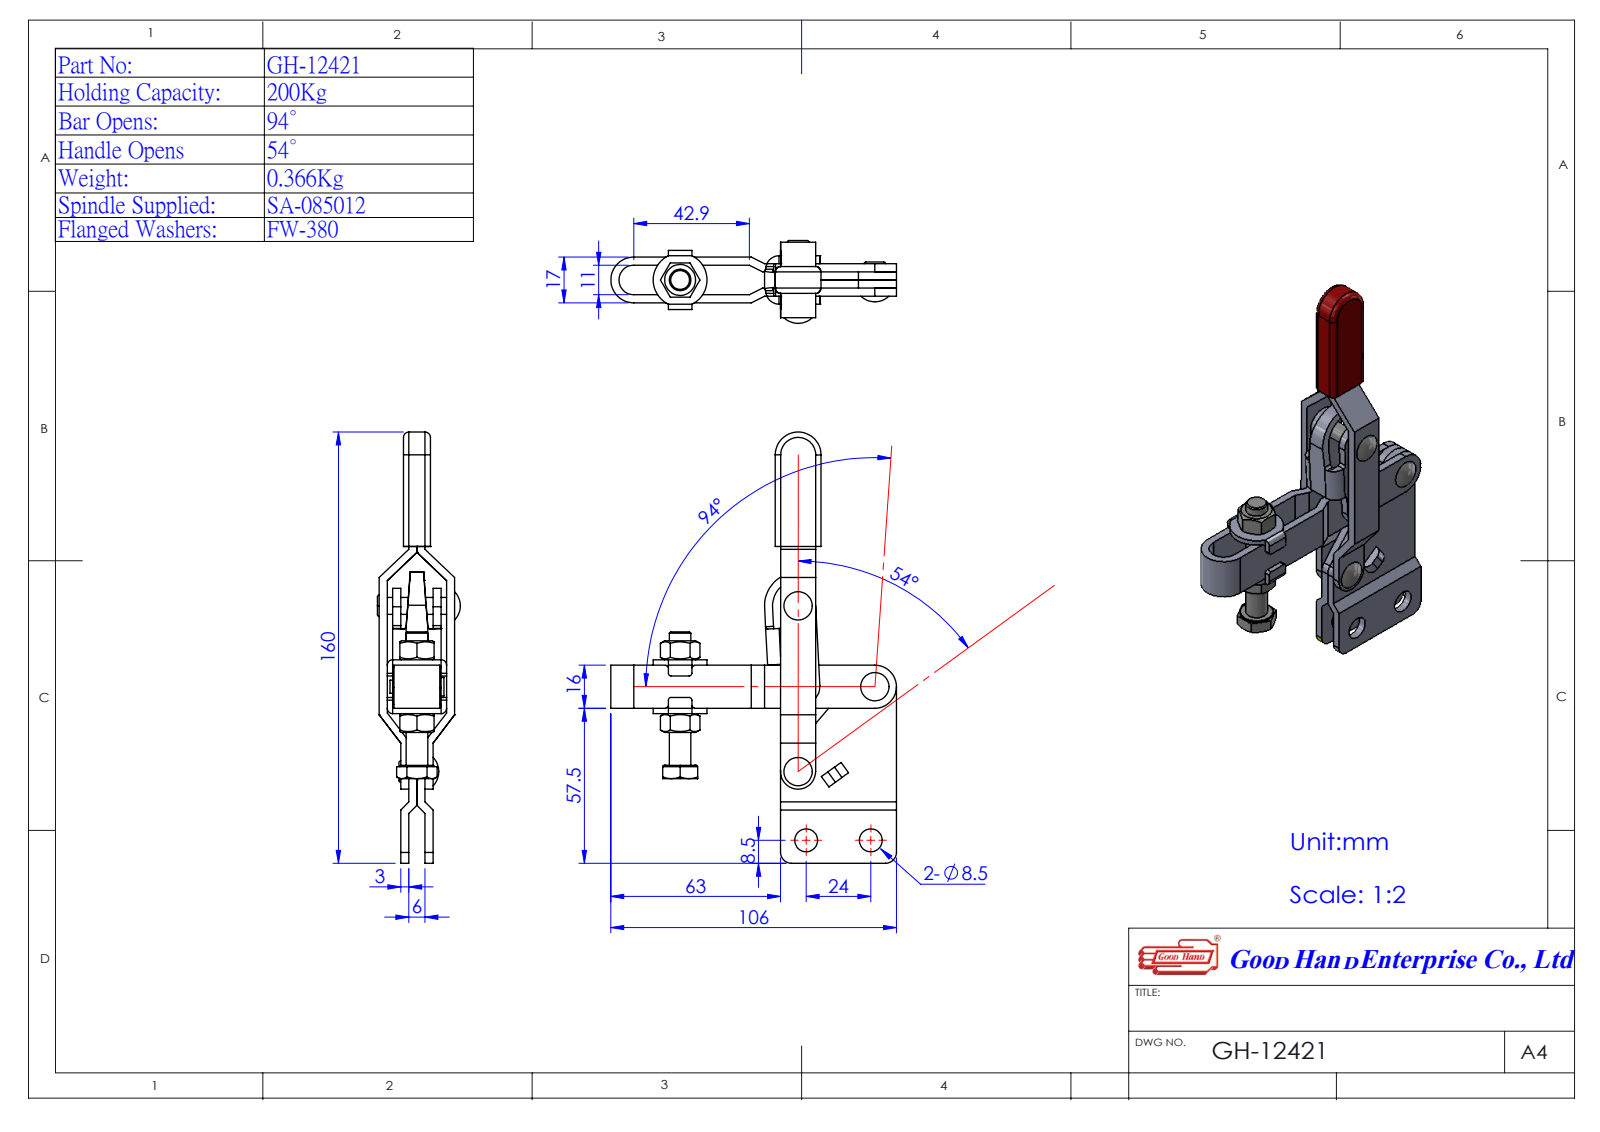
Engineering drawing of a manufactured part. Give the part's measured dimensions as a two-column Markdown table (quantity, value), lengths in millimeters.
| quantity | value |
| --- | --- |
| part name | Group1^GH-12421(簡化); Group2^GH-12421(簡化); Group3^GH-12421(簡化); Group5^GH-12421(簡化) (+2 more) |
| STEP written by | SolidWorks 2016 (AUTOMOTIVE_DESIGN) |
| units | millimeters |
| bodies | 5 solids, 260 faces (139 planar, 95 cylindrical, 26 other) |
| overall size | 159.5 × 106 × 30.77 |
| volume | 50 038 mm³ |
| surface area | 36 143 mm² |
| round holes (diameter × count) | 4 × 4, 8.5 × 2 |
| round bosses / shafts (diameter × count) | 4.83 × 2, 12.5 × 1, 8 × 1, 6 × 1, 4.85 × 1 |
| partial cylindrical surfaces (radius × count) | 1 × 12, 2 × 4, 5 × 3, 6.5 × 3, 4 × 2, 8.5 × 2, 5.5 × 1, 8 × 1 |
| main face-to-face distances | 3, 6, 9, 5.5, 14, 11, 2.5, 8, 8.5, 5 |
| hole center spacings | 57.02, 24, 25.68, 26.93, 30.04, 31.54, 37.14, 41.37 |
